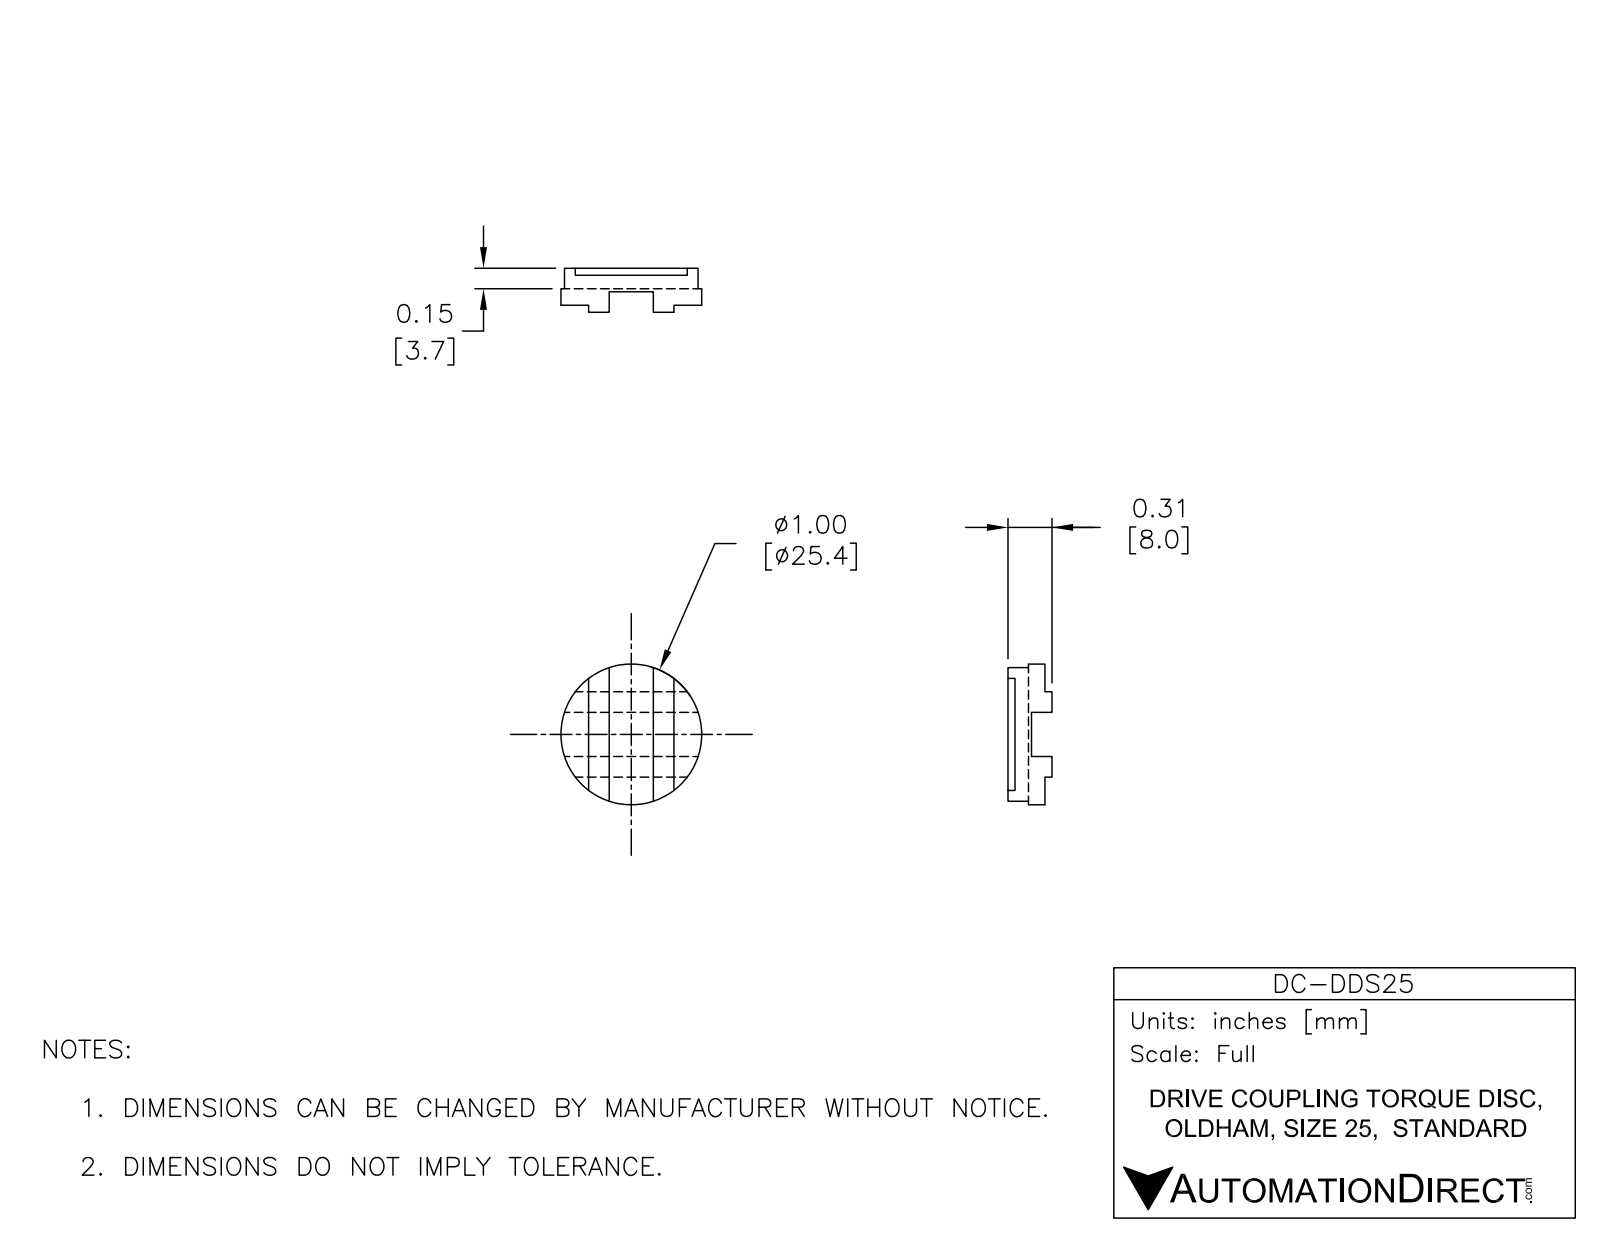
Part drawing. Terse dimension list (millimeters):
name: DC-DDS25
written by: SolidWorks 2015 (AUTOMOTIVE_DESIGN)
unit: mm
bodies: 1 solid, 20 faces (18 planar, 2 cylindrical, 0 other)
size: 25.4 × 25.4 × 7.95
volume: 2 192 mm³; area: 1 869 mm²
bosses: 1× ⌀25.4
face distances: 3.71, 4.24, 1.27, 6.68, 2.44, 2.97, 0.53, 7.98, 7.95, 5.41
